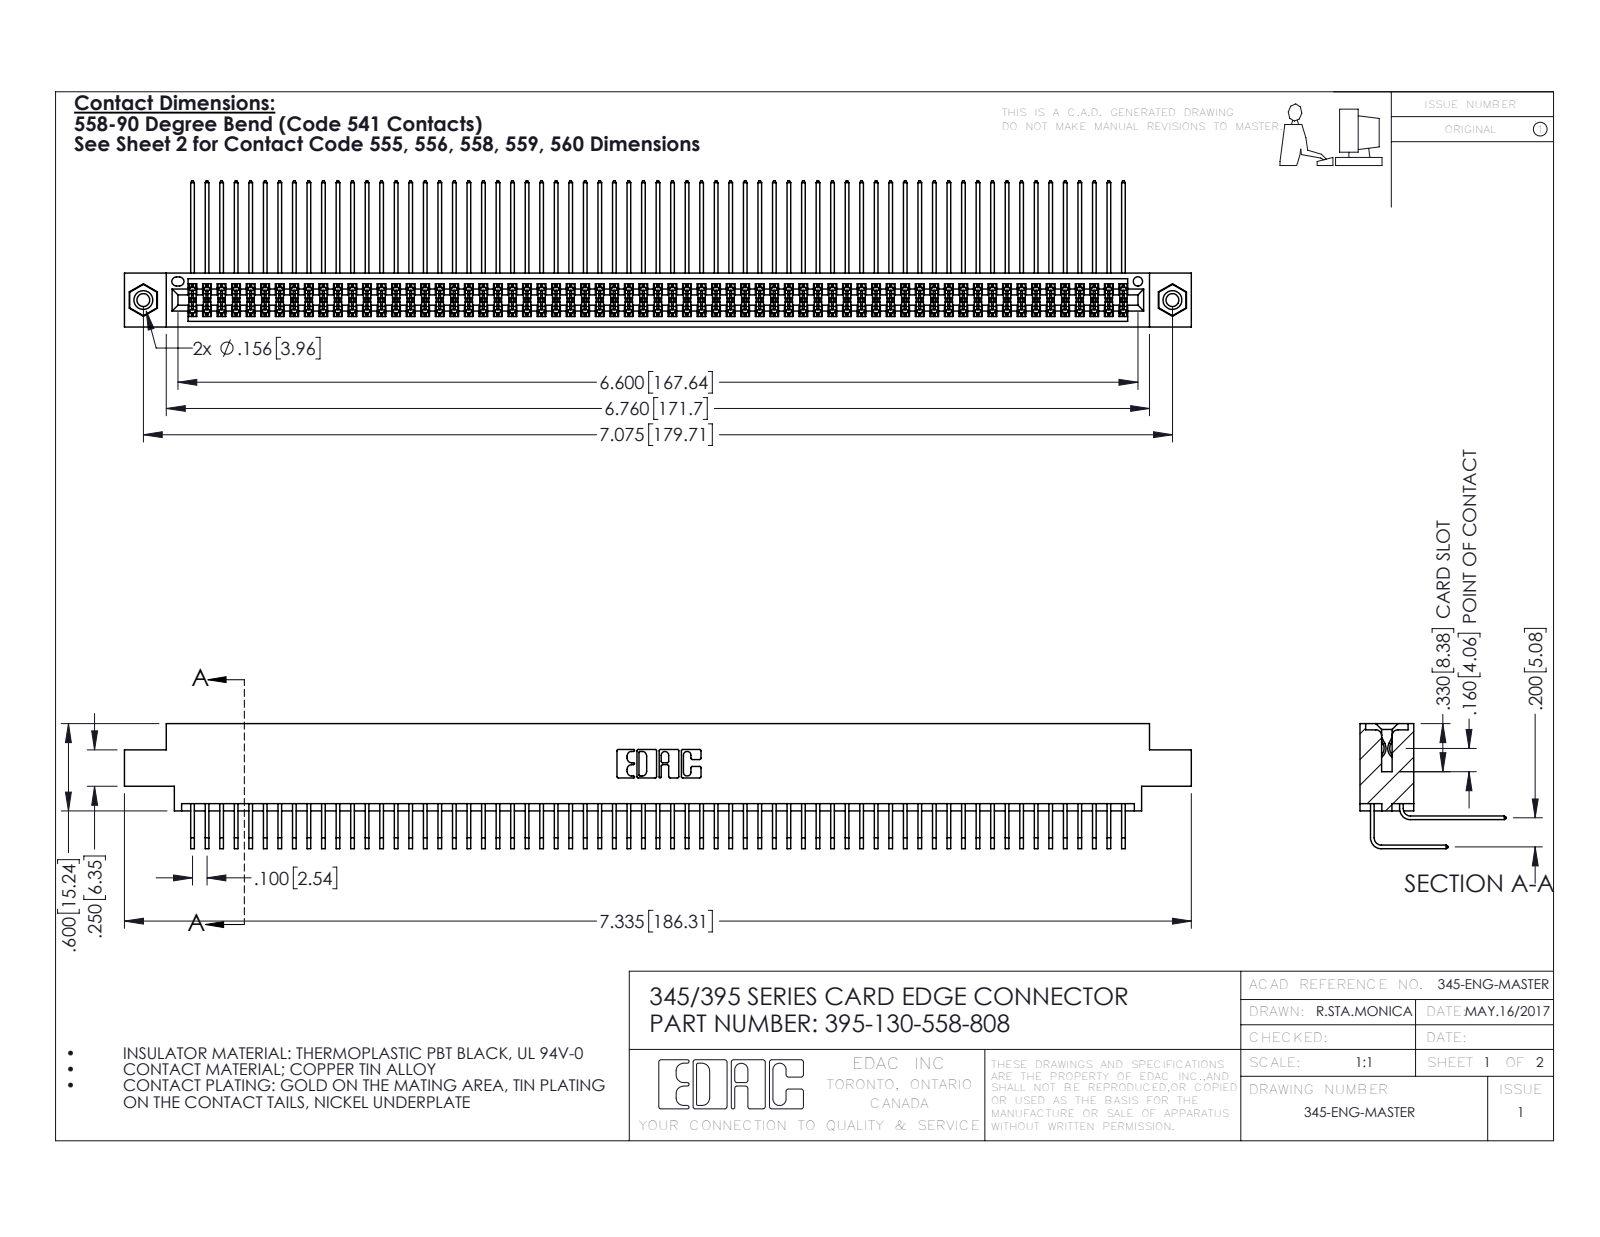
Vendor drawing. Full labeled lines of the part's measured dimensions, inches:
Part name (STEP PRODUCT): 345 Part_0.170 Offset - 0.156 Dia-TI; 345-292-001_558 Tail - 2; 345-292-001_558 559 Tail - 1; 345-250-001_345-250-003-102 (+1 more)
STEP written by: SolidWorks 2016 (CONFIG_CONTROL_DESIGN)
Units: inches
Bodies: 133 solids, 6950 faces (4666 planar, 2268 cylindrical, 16 other)
Overall size (bounding box): 7.335 × 1.005 × 0.859
Volume: 1.156 in³ · Surface area: 49.8 in²
Round holes (diameter × count): ⌀0.089 ×2, ⌀0.125 ×2, ⌀0.156 ×2, ⌀0.064 ×1
Round bosses / shafts (diameter × count): ⌀0.155 ×2
Partial cylindrical surfaces — rounded edges, fillets, slot ends (radius × count): R0.006 ×196, R0.01 ×22, R0.007 ×6, R0.031 ×6, R0.026 ×3, R0.014 ×2, R0.019 ×2, R0.022 ×2
Main face-to-face distances: 0.072, 0.298, 0.2, 0.37, 0.098, 0.272, 0.025, 0.225, 0.175, 0.025
Hole centre spacings: 0.27, 6.839, 7.075
